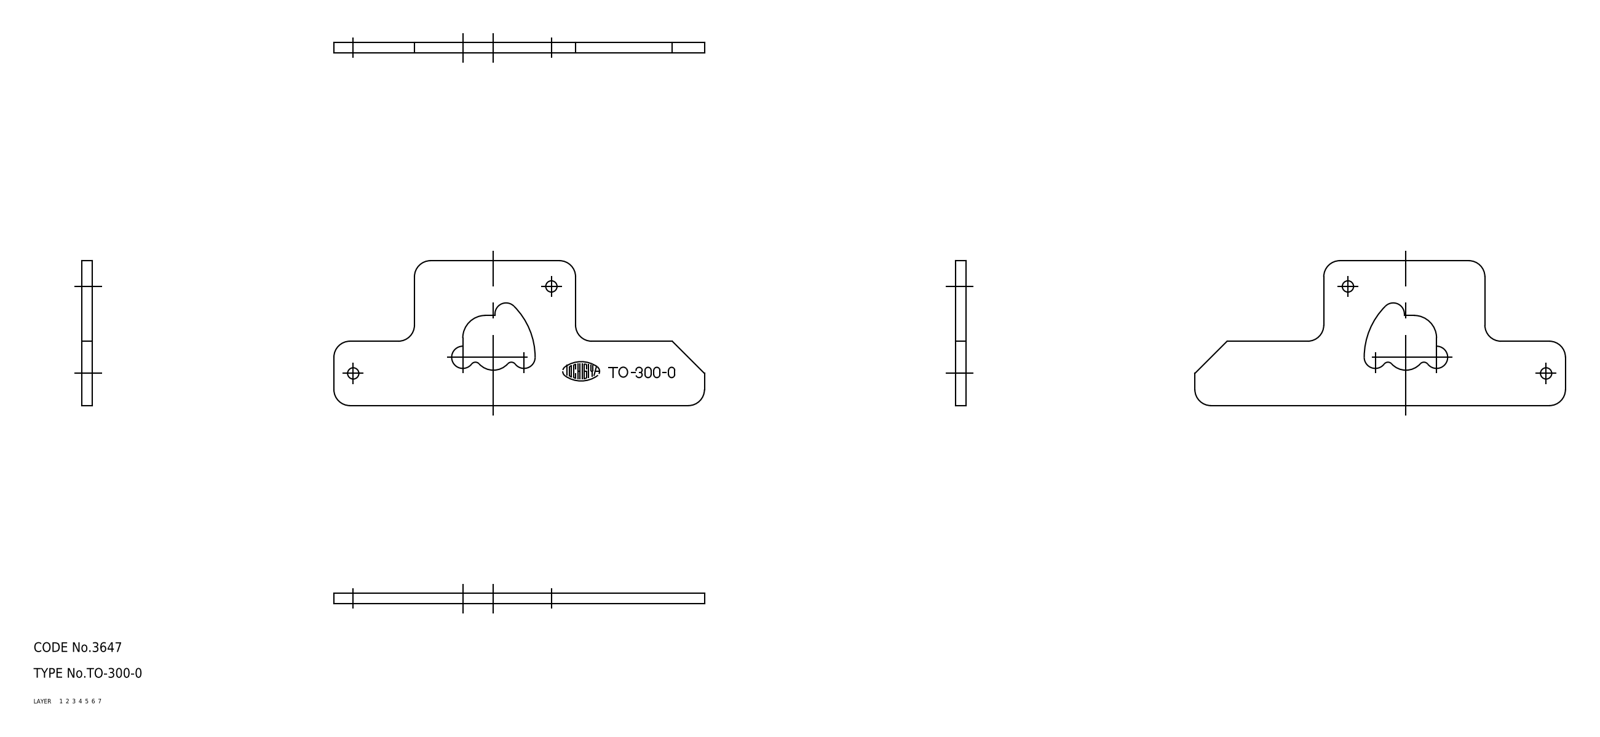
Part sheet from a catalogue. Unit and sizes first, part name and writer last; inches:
Units: inches
Overall size (bounding box): 4.528 × 1.772 × 0.126
Volume: 0.604 in³ · Surface area: 11.59 in²
Bodies: 1 solid, 33 faces (0 planar, 0 cylindrical, 33 other)
Part name (STEP PRODUCT): cam
STEP written by: CADfix (AUTOMOTIVE_DESIGN)
